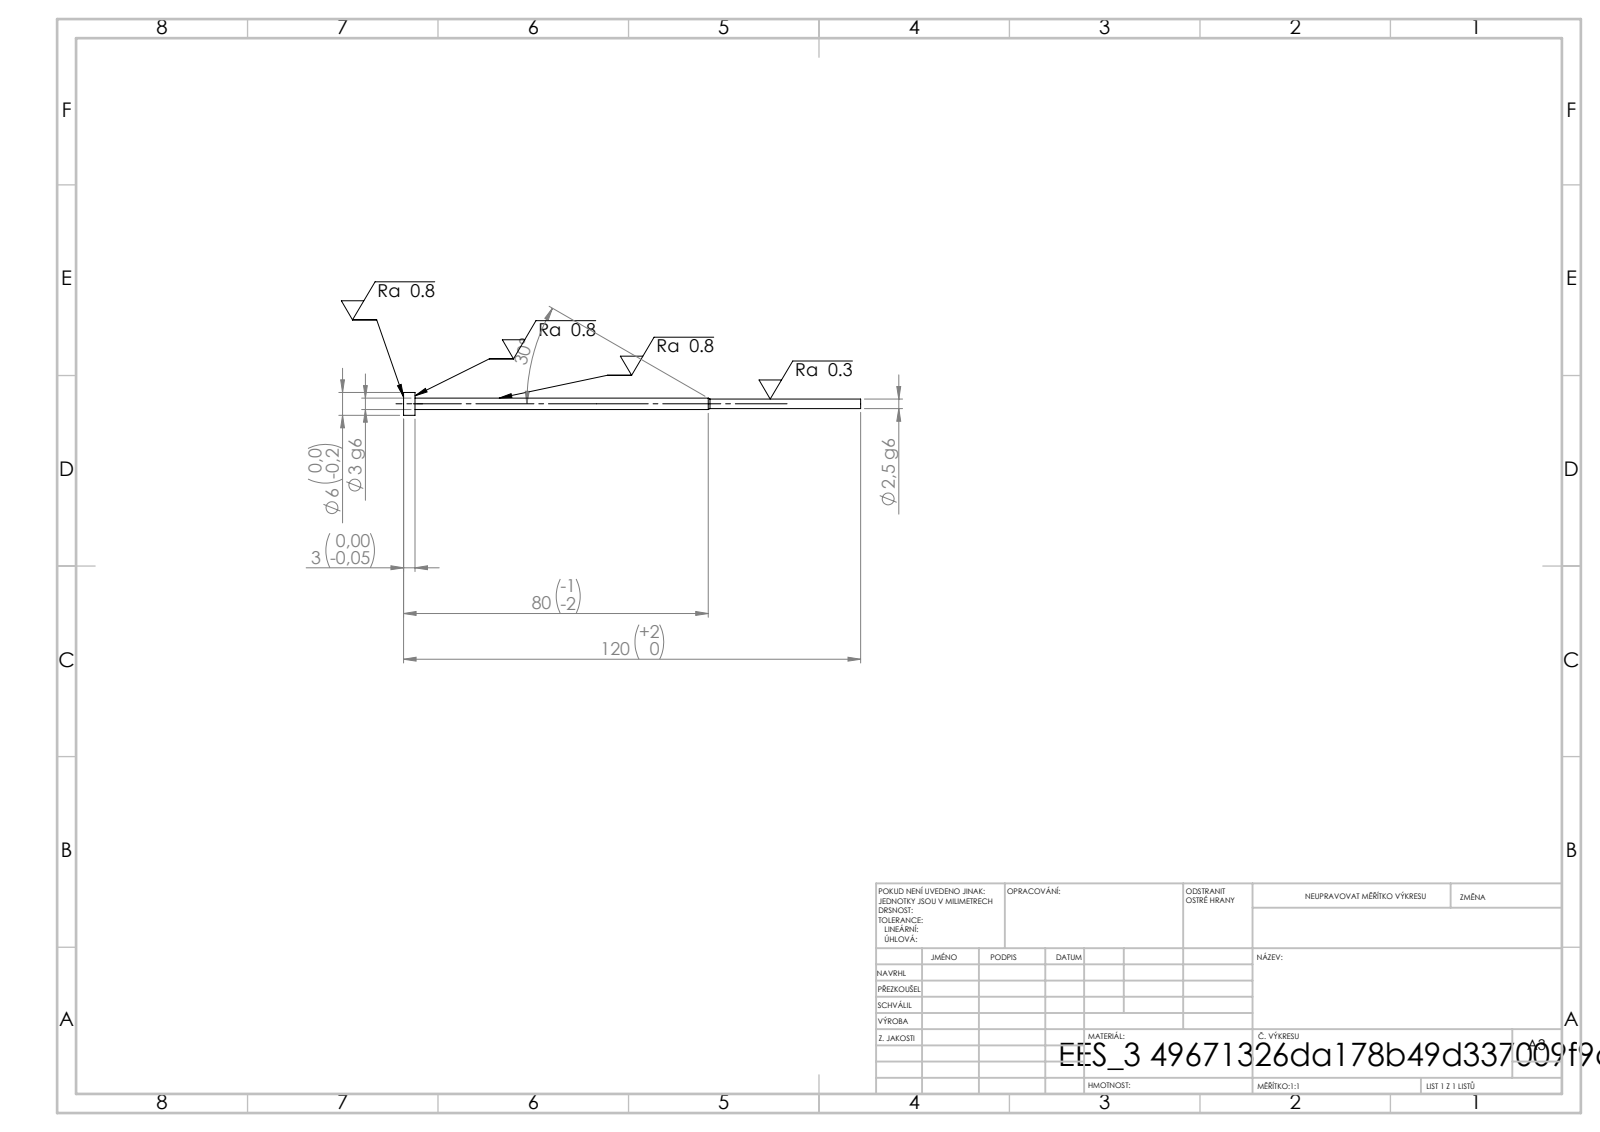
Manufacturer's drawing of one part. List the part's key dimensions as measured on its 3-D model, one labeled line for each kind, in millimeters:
STEP written by: SolidWorks 2019 (CONFIG_CONTROL_DESIGN)
Units: millimetres
Bodies: 1 solid, 11 faces (3 planar, 6 cylindrical, 2 other)
Overall size (bounding box): 120 × 6 × 6
Volume: 826 mm³ · Surface area: 1 152 mm²
Round bosses / shafts (diameter × count): ⌀6 ×1, ⌀3 ×1, ⌀2.5 ×1
Main face-to-face distances: 3, 117, 120
